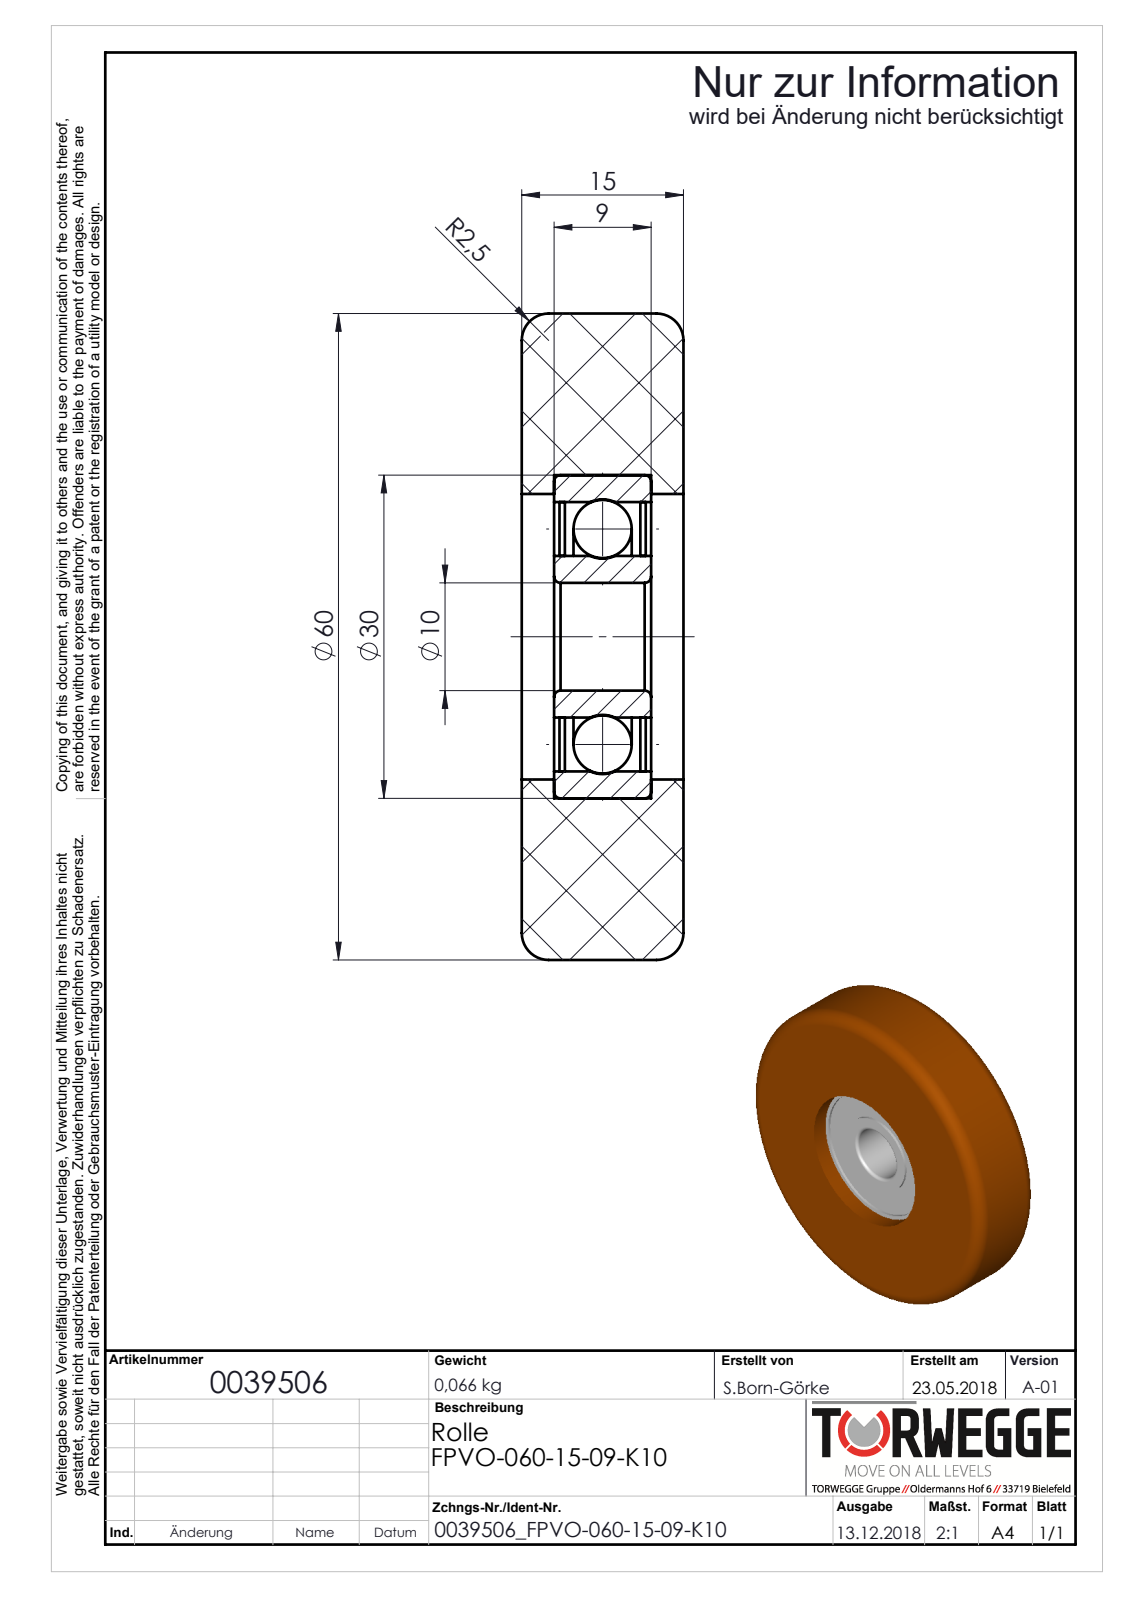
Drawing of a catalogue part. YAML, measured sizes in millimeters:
part_name: "DIN625_TF_0033512_DIN625-6200-ZZ; 0039506-Bandage; 0039506_FPVO-060-15-09-K10_(A-01)"
step_written_by: "SolidWorks 2018 (AUTOMOTIVE_DESIGN)"
units: millimeters
bodies: {solids: 6, faces: 62, planar: 12, cylindrical: 28, other: 22}
overall_size: [60, 60, 15]
volume: 36757
surface_area: 13910
round_holes:
  - {diameter: 10, count: 1}
  - {diameter: 15, count: 1}
  - {diameter: 25, count: 1}
  - {diameter: 26.5, count: 1}
  - {diameter: 30, count: 1}
round_bosses_or_shafts:
  - {diameter: 60, count: 1}
face_to_face_distances: [15, 0.5, 8, 3, 12, 3.5, 4, 11, 11.5, 1]
